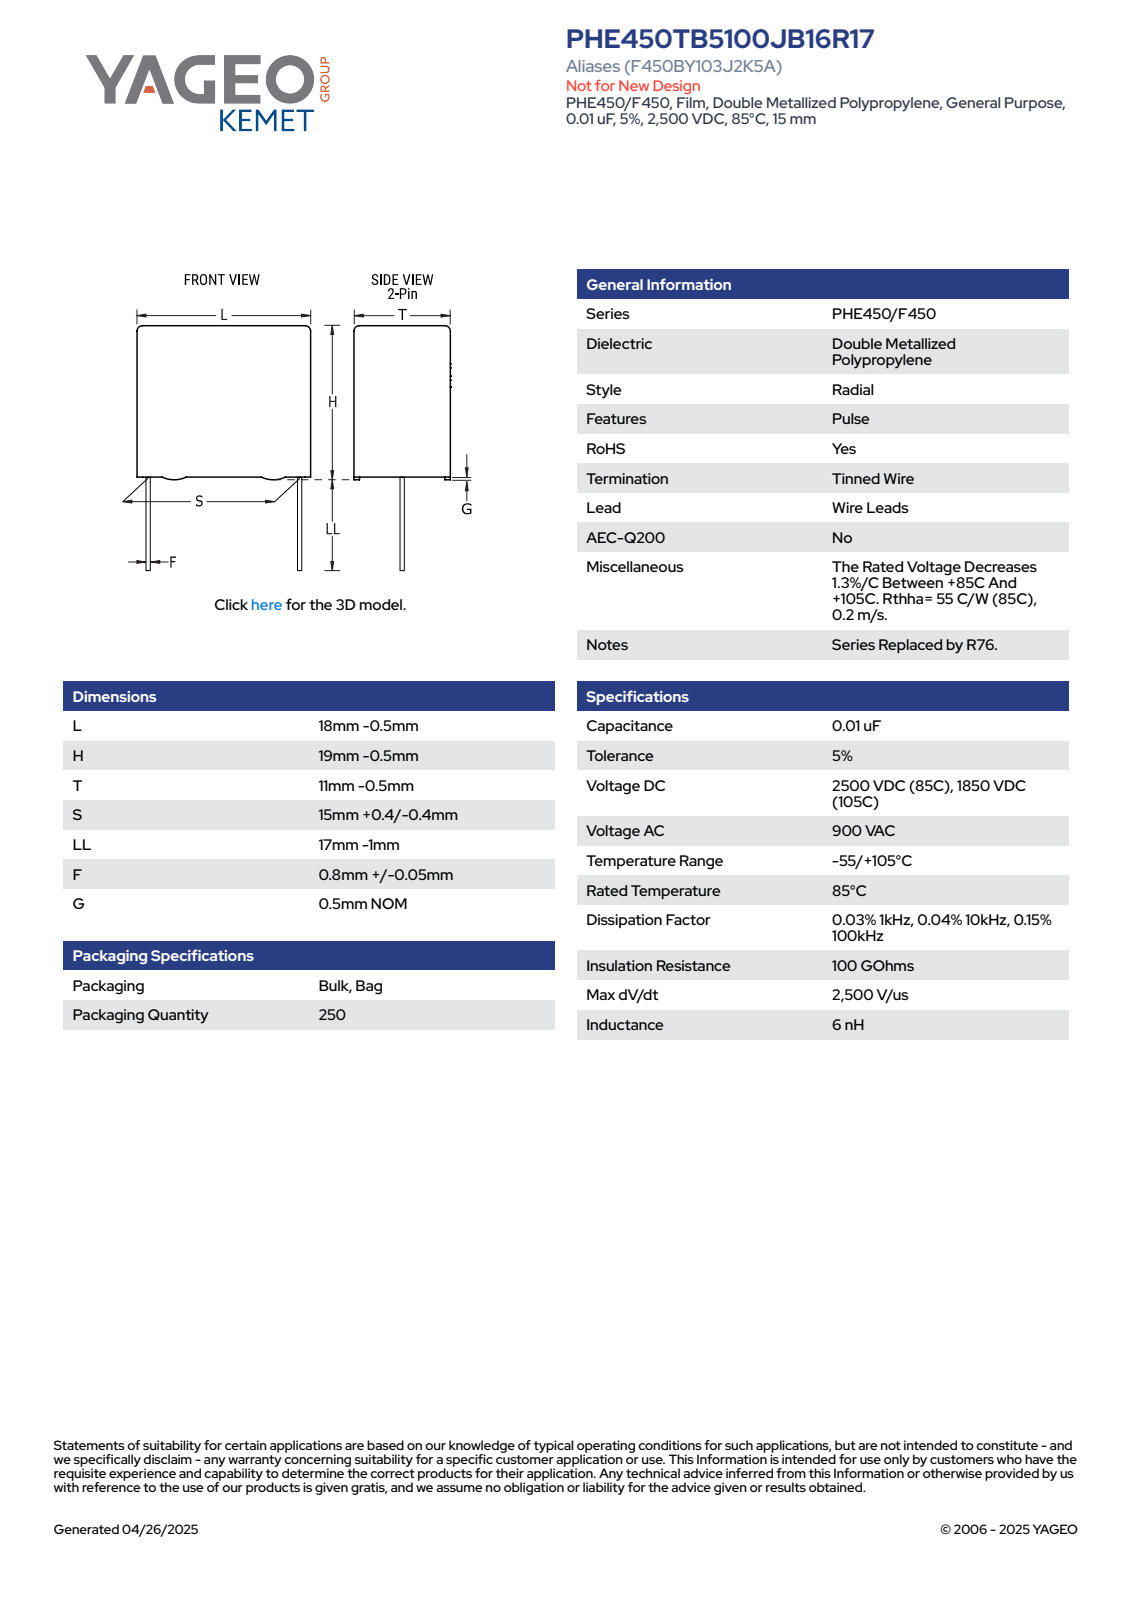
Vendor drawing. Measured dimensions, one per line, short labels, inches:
name: CFR_RBG_18X19X11_L17.5H18.5T10.5S15LL16F0.85G0.5
written by: SolidWorks 2014 (AUTOMOTIVE_DESIGN)
unit: in
bodies: 4 solids, 89 faces (81 planar, 8 cylindrical, 0 other)
size: 1.358 × 0.689 × 0.414
volume: 0.203 in³; area: 2.322 in²
bosses: 2× ⌀0.033
rounds: 4× R0.02
face distances: 0.413, 0.689, 0.709, 0.414, 0.02, 0.728, 0.024, 0.39, 0.024, 0.366
